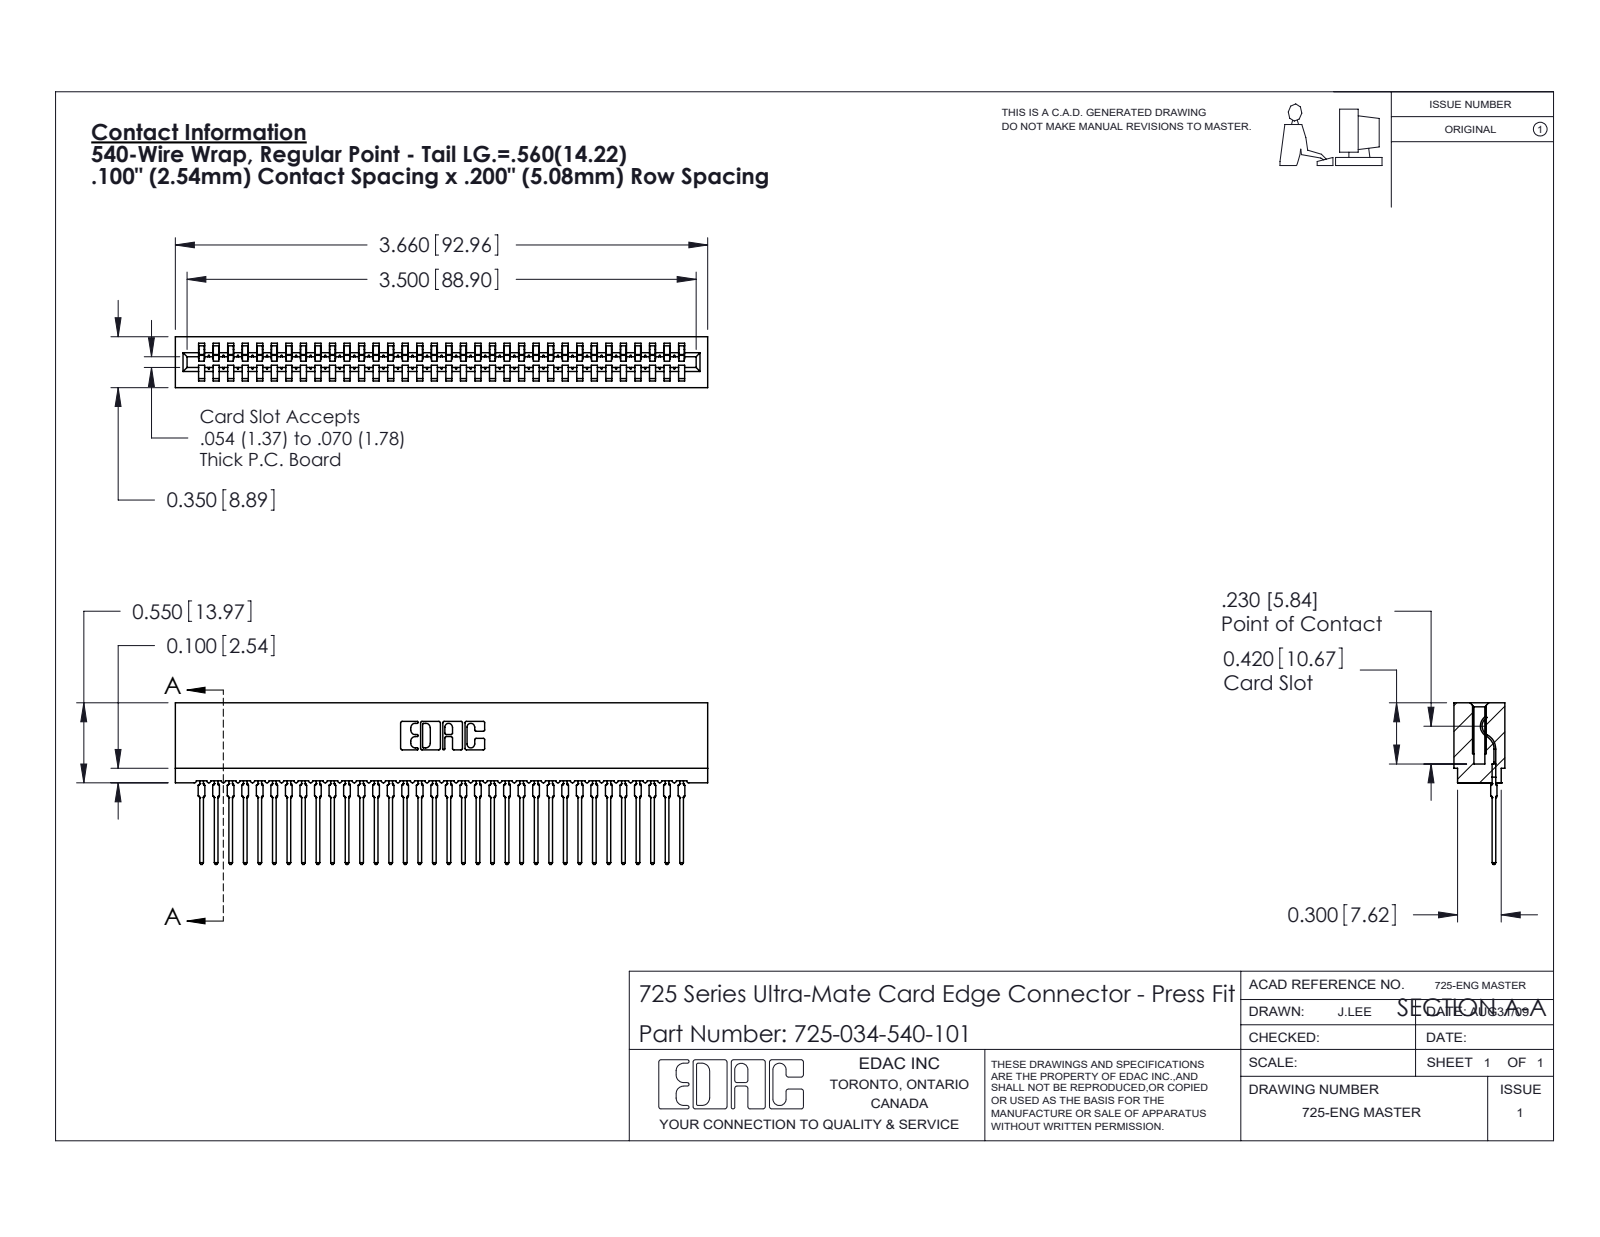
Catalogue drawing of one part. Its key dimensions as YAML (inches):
part_name: "725 Part_Insulator Option - 01; 725-034-540-101; 745-292-001_540"
step_written_by: "SolidWorks 2020 (CONFIG_CONTROL_DESIGN)"
units: inches
bodies: {solids: 35, faces: 3903, planar: 2333, cylindrical: 686, other: 884}
overall_size: [3.66, 1.111, 0.35]
volume: 0.438
surface_area: 21.77
partial_cylinders:
  - {radius: 0.015, count: 68}
  - {radius: 0.021, count: 68}
  - {radius: 0.01, count: 22}
  - {radius: 0.007, count: 6}
  - {radius: 0.031, count: 6}
  - {radius: 0.005, count: 4}
  - {radius: 0.011, count: 4}
  - {radius: 0.026, count: 3}
face_to_face_distances: [0.2, 0.1, 0.35, 0.3, 0.212, 0.138, 0.063, 0.287, 0.4, 0.5]
